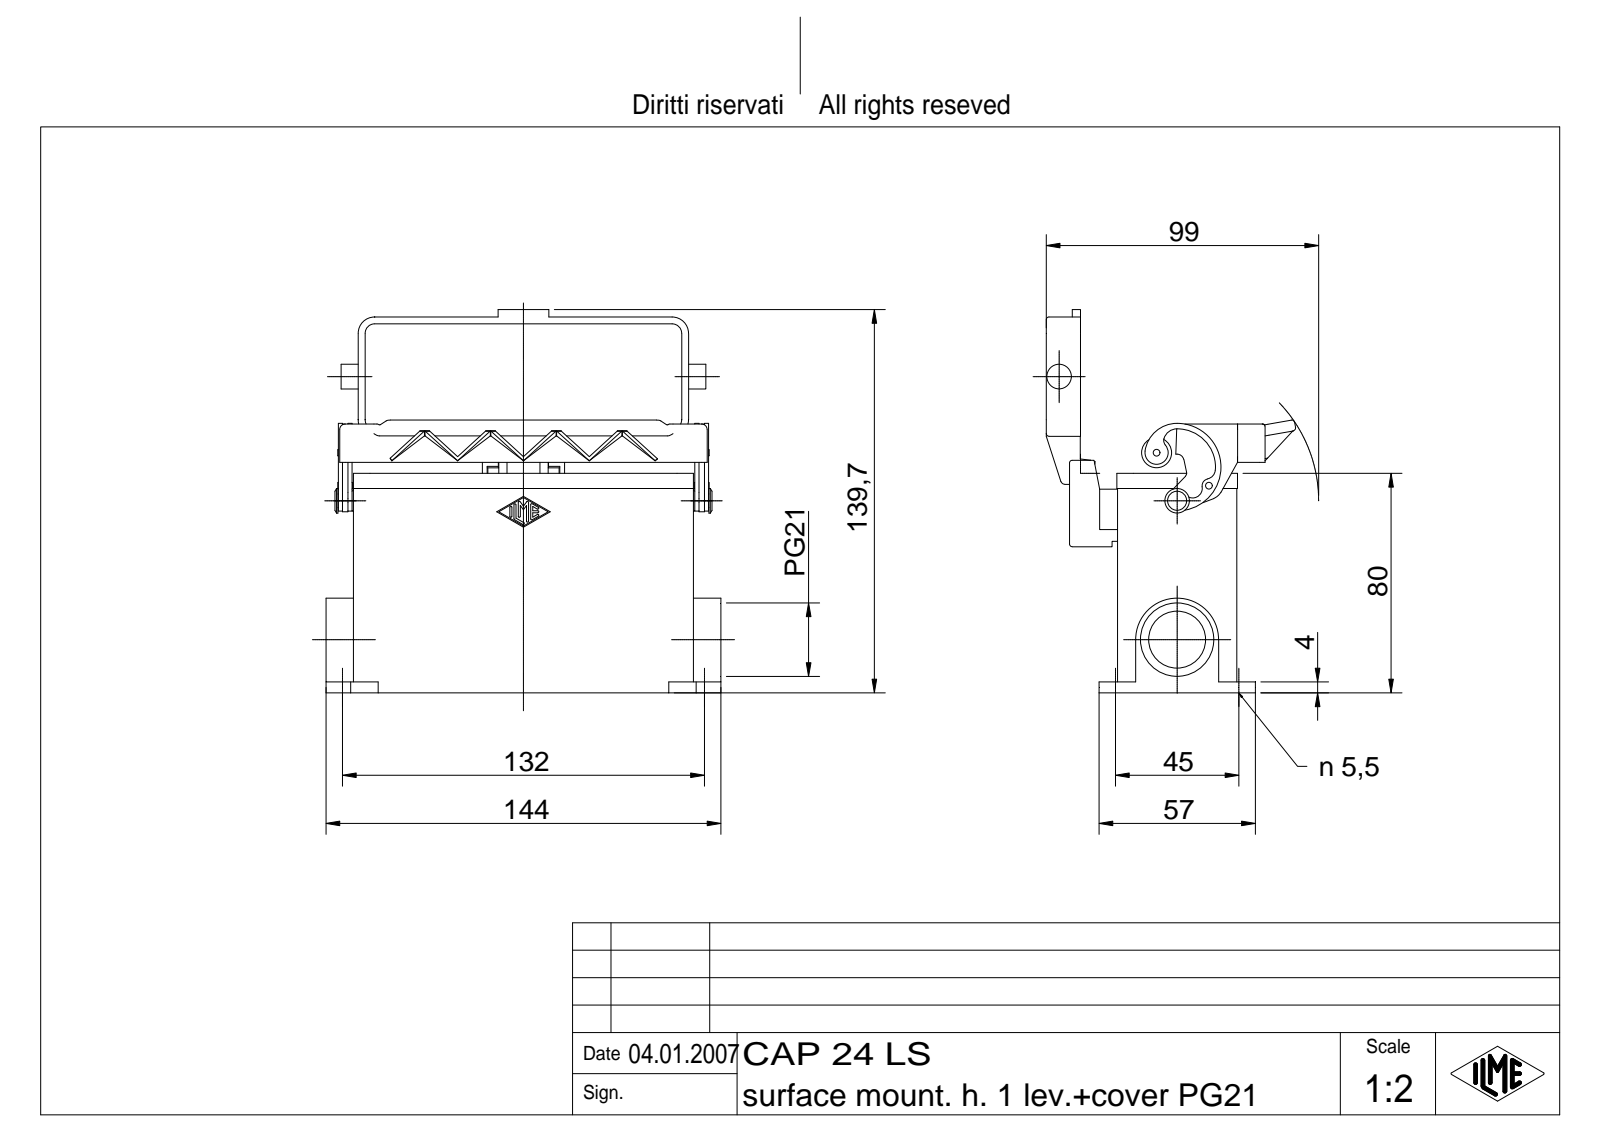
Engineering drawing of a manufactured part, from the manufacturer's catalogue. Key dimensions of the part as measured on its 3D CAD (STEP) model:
Part name (STEP PRODUCT): CAP 24 LS
STEP written by: Autodesk Inventor 7 (AUTOMOTIVE_DESIGN)
Units: millimetres
Bodies: 6 solids, 623 faces (279 planar, 180 cylindrical, 164 other)
Overall size (bounding box): 144 × 139.7 × 90.95
Volume: 193 257 mm³ · Surface area: 106 964 mm²
Round holes (diameter × count): ⌀5.5 ×4, ⌀2 ×1, ⌀4 ×1, ⌀20.78 ×1, ⌀26.78 ×1
Round bosses / shafts (diameter × count): ⌀9 ×2, ⌀5 ×2, ⌀11 ×1, ⌀7 ×1, ⌀4 ×1, ⌀3 ×1, ⌀2.5 ×1
Partial cylindrical surfaces — rounded edges, fillets, slot ends (radius × count): R1 ×18, R0.38 ×14, R2 ×12, R6 ×12, R1.5 ×6, R3.5 ×6, R3 ×4, R0.5 ×3
Main face-to-face distances: 3, 40.5, 43.5, 4, 37.5, 26, 66.5, 69.5, 29, 3.5
Hole centre spacings: 45, 132, 139.46, 57.3
